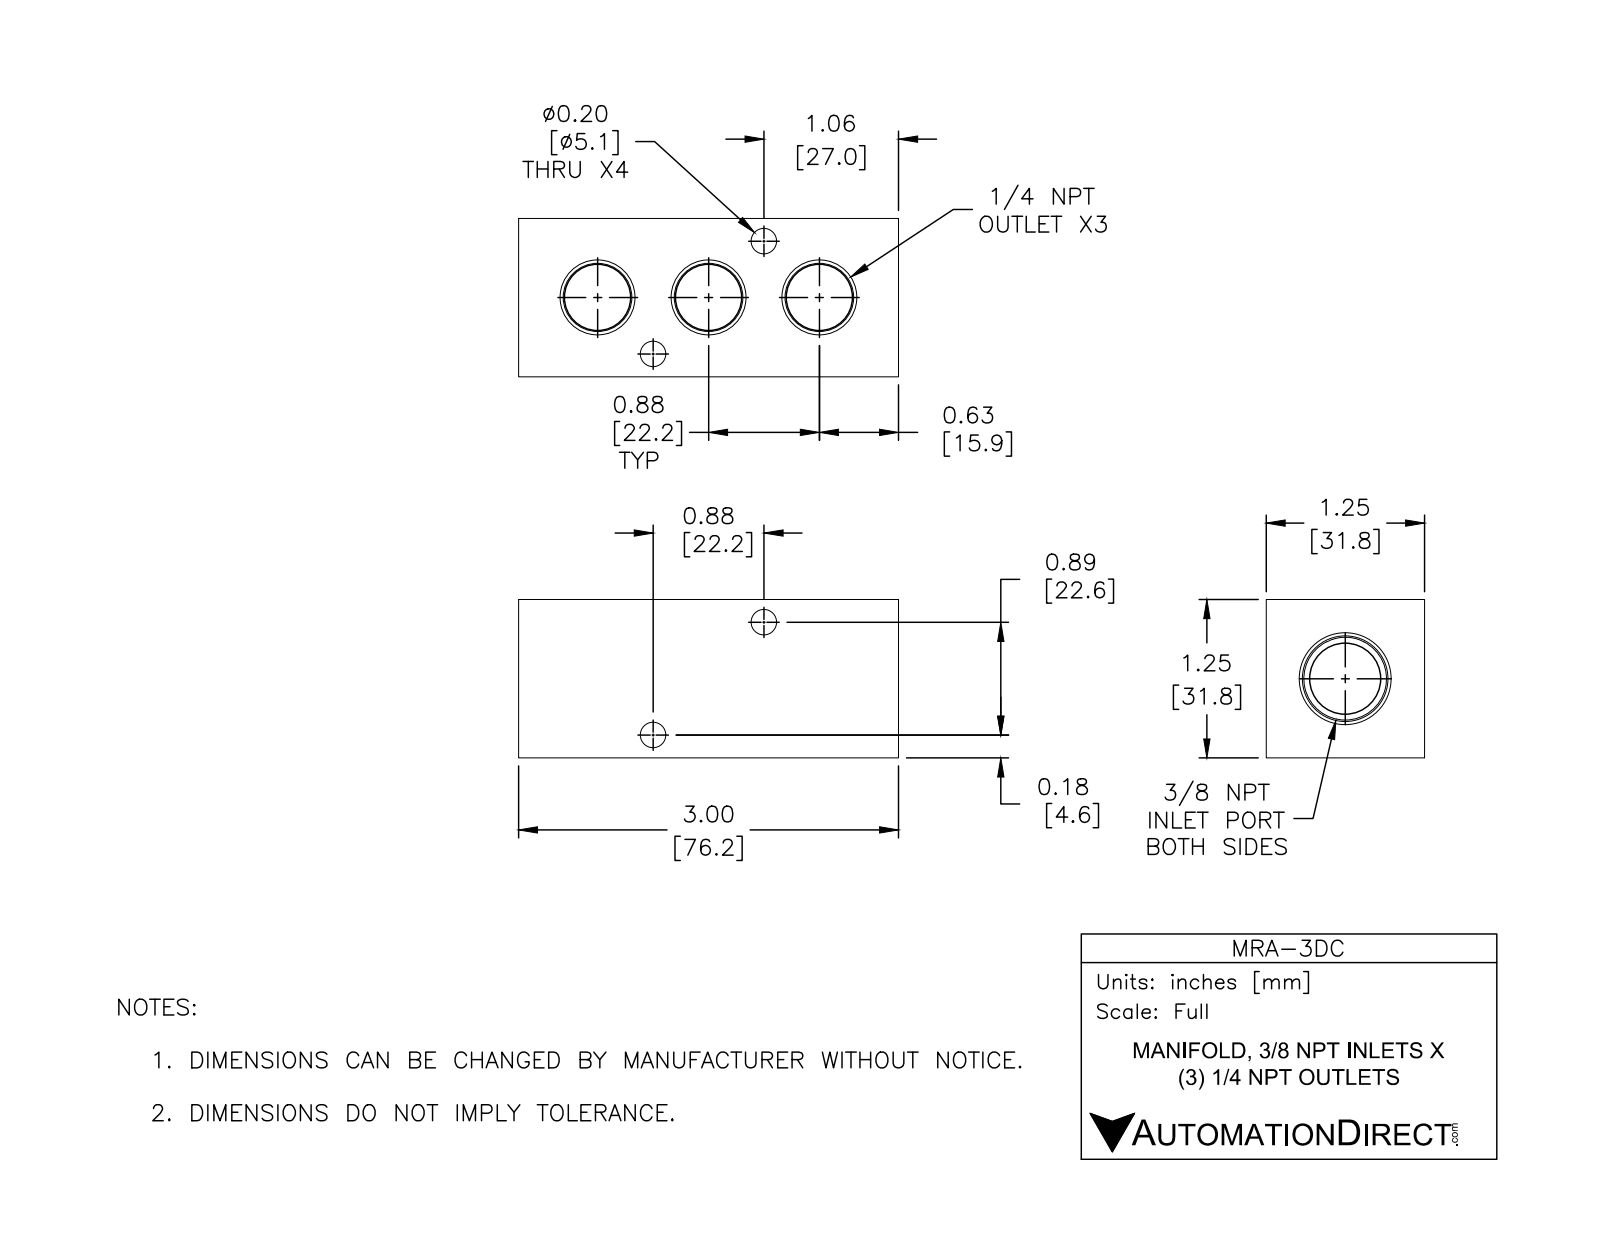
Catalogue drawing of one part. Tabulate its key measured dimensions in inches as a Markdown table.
| quantity | value |
| --- | --- |
| part name | MRA-3DC |
| STEP written by | SolidWorks 2015 (CONFIG_CONTROL_DESIGN) |
| units | inches |
| bodies | 1 solid, 58 faces (14 planar, 24 cylindrical, 20 other) |
| overall size | 3 × 1.25 × 1.25 |
| volume | 3.469 in³ |
| surface area | 26.31 in² |
| round holes (diameter × count) | 0.2 × 4, 0.562 × 1 |
| partial cylindrical surfaces (radius × count) | 0.219 × 3 |
| main face-to-face distances | 1.25, 3, 0.41, 2.59, 0.86, 0.39, 2.18 |
| hole center spacings | 1.248 |
